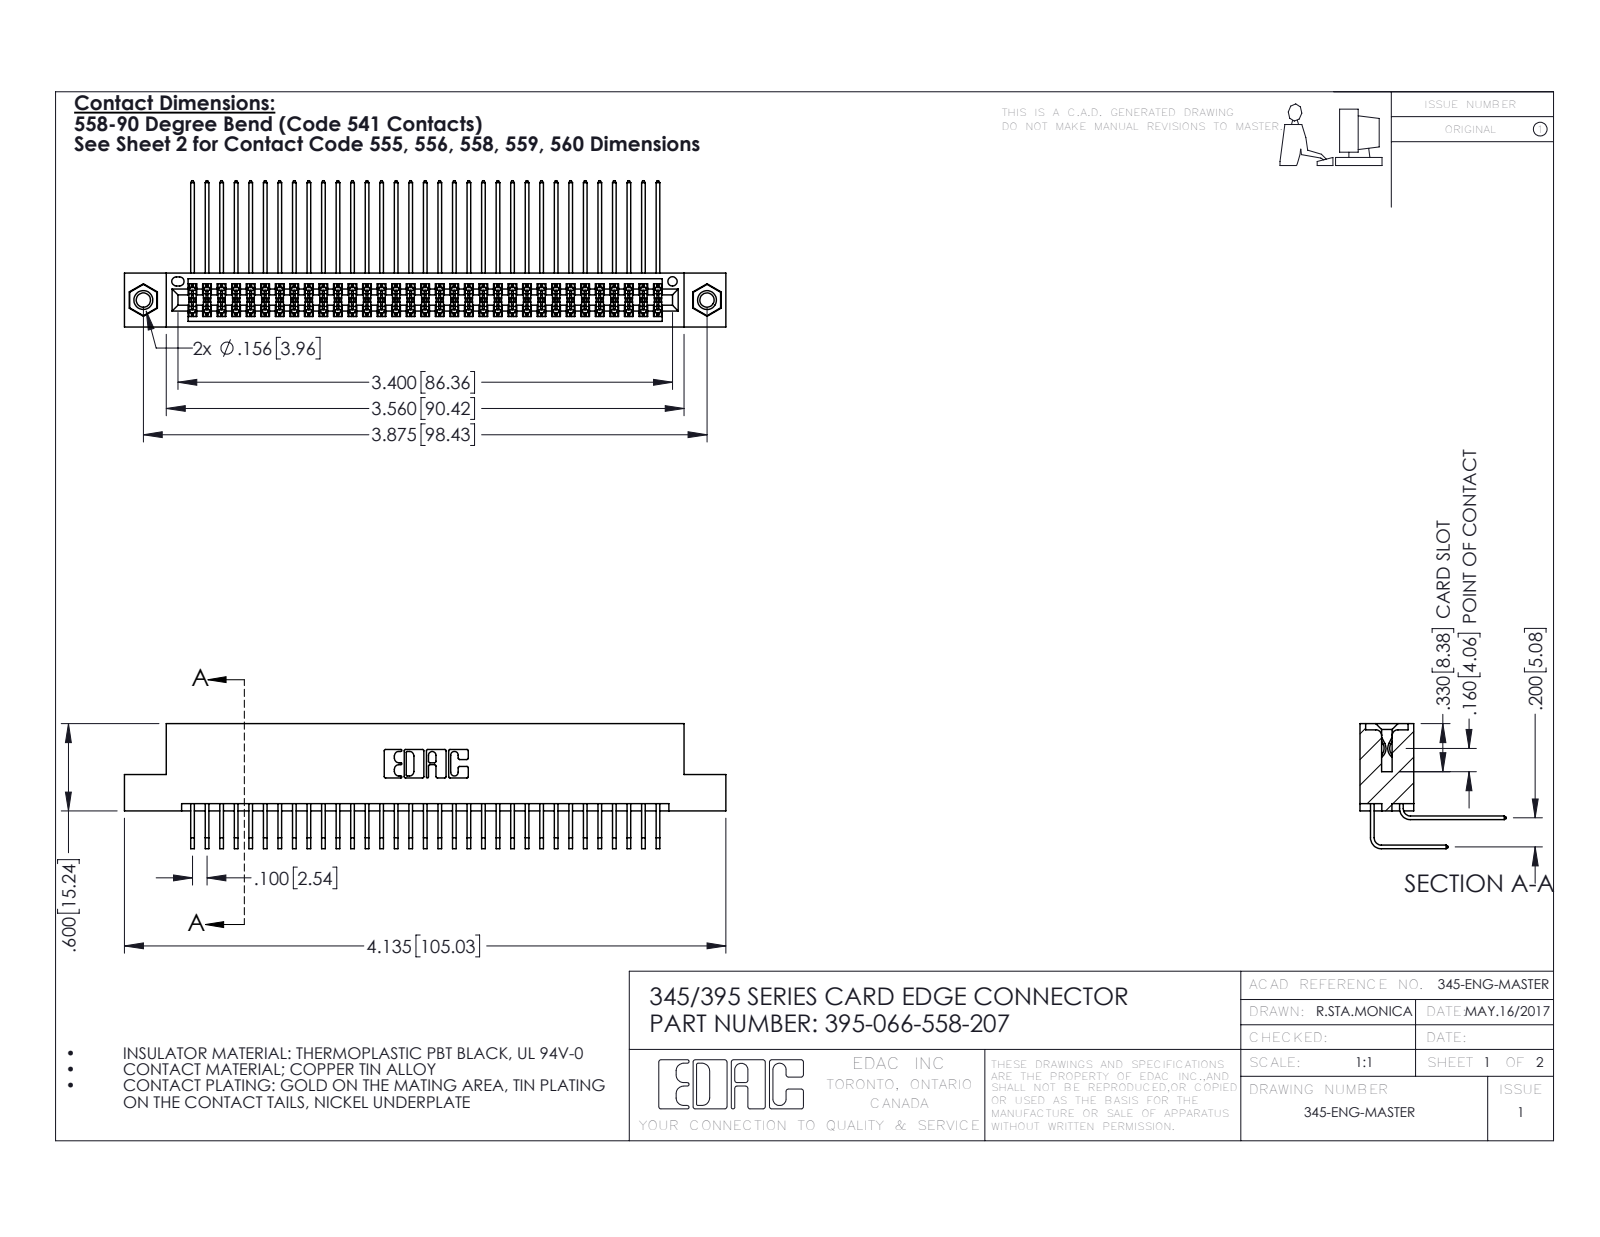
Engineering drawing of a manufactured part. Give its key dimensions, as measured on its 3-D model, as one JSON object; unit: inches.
{"part_name": "345 Part_Flush Mounting Lugs - 0.156 Dia-TI; 345-250-001_345-250-005-103; 345-292-001_558 Tail - 2; 395-066-558-207 (+1 more)", "step_written_by": "SolidWorks 2016 (CONFIG_CONTROL_DESIGN)", "units": "inches", "bodies": {"solids": 69, "faces": 3618, "planar": 2422, "cylindrical": 1180, "other": 16}, "overall_size": [4.135, 1.005, 0.859], "volume_in3": 0.64, "surface_area_in2": 26.57, "round_holes": [[0.098, 2], [0.125, 2], [0.156, 2], [0.064, 1]], "round_bosses_or_shafts": [[0.155, 2]], "partial_cylinders_radius": [[0.006, 100], [0.01, 22], [0.007, 6], [0.031, 6], [0.026, 3], [0.014, 2], [0.019, 2], [0.022, 2]], "face_to_face_distances": [0.2, 0.072, 0.298, 0.37, 0.098, 0.272, 0.025, 0.225, 0.025, 0.175], "hole_center_spacings": [0.27, 3.64, 3.875]}
